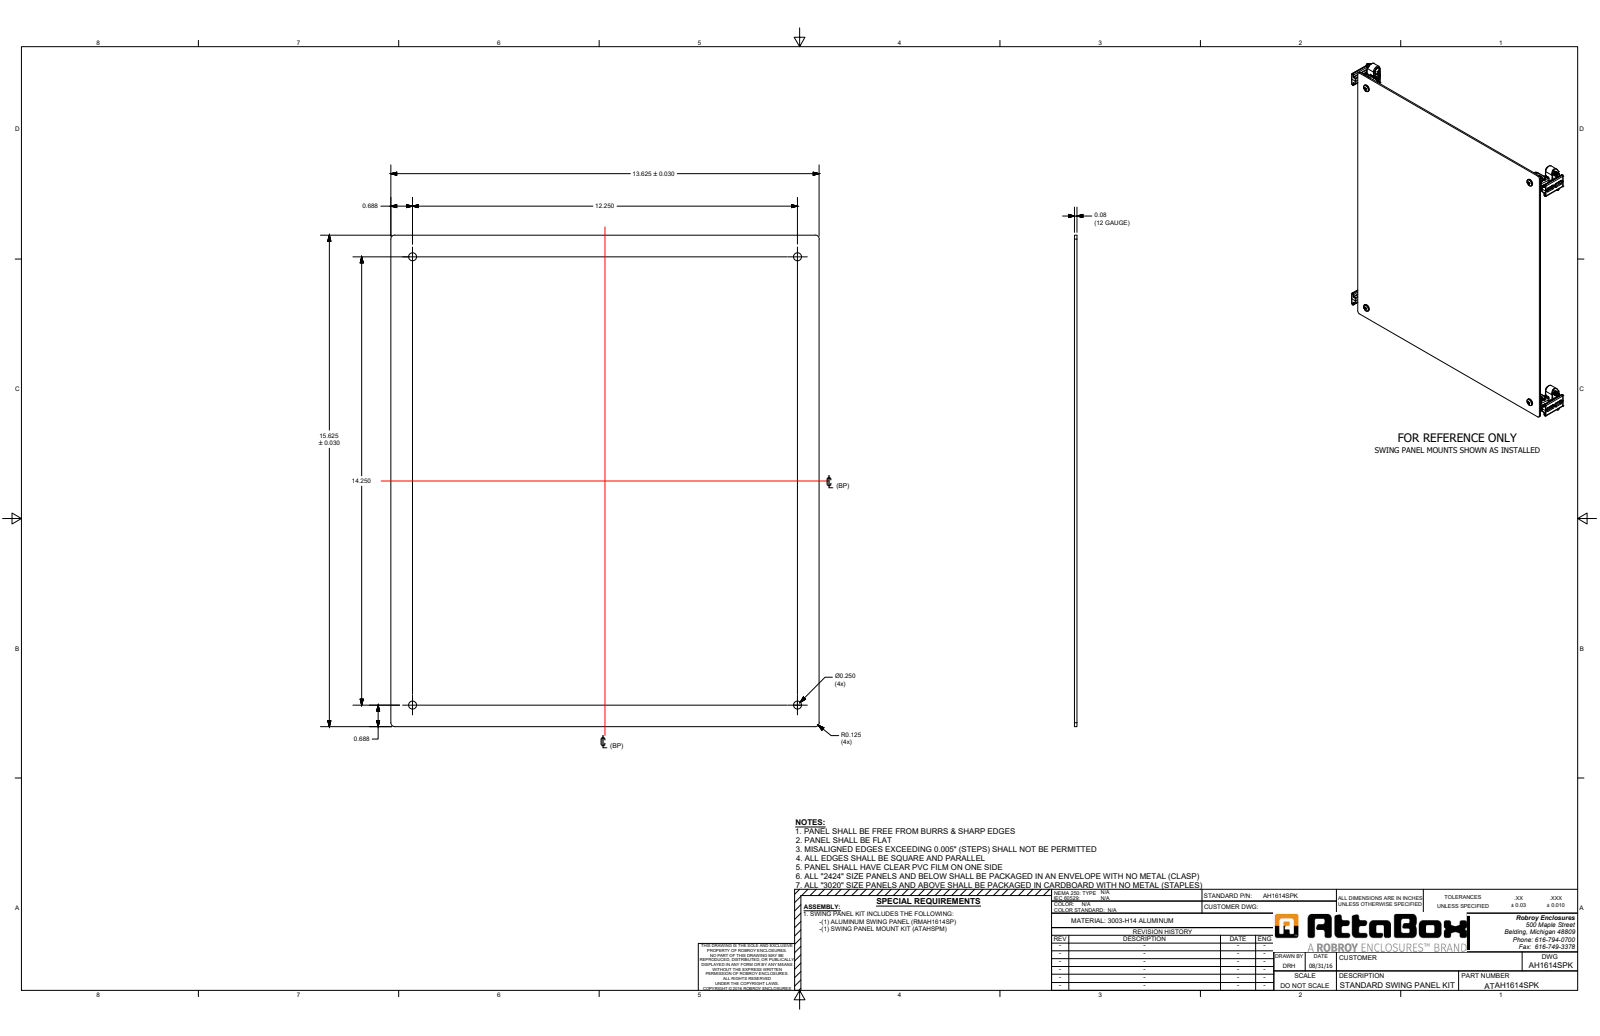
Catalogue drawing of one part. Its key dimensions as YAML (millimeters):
part_name: "AH1614SPK"
step_written_by: "SolidWorks 2019 (AUTOMOTIVE_DESIGN)"
units: millimeters
bodies: {solids: 33, faces: 2010, planar: 518, cylindrical: 736, other: 756}
overall_size: [396.9, 369.8, 36.8]
volume: 329400
surface_area: 314700
round_holes:
  - {diameter: 4, count: 8}
  - {diameter: 6.4, count: 8}
round_bosses_or_shafts:
  - {diameter: 9.5, count: 8}
  - {diameter: 6.7, count: 8}
  - {diameter: 4.8, count: 8}
partial_cylinders:
  - {radius: 0.9, count: 248}
  - {radius: 0.5, count: 124}
  - {radius: 1.7, count: 54}
  - {radius: 0.4, count: 30}
  - {radius: 1.1, count: 16}
  - {radius: 1.3, count: 16}
  - {radius: 0.6, count: 14}
  - {radius: 22.9, count: 8}
face_to_face_distances: [2, 362, 6.1, 6.2, 12.7, 346.1, 13, 15, 369.8, 396.9]
hole_center_spacings: [362, 22.2, 311.2, 477.3, 339.7, 384.2]
